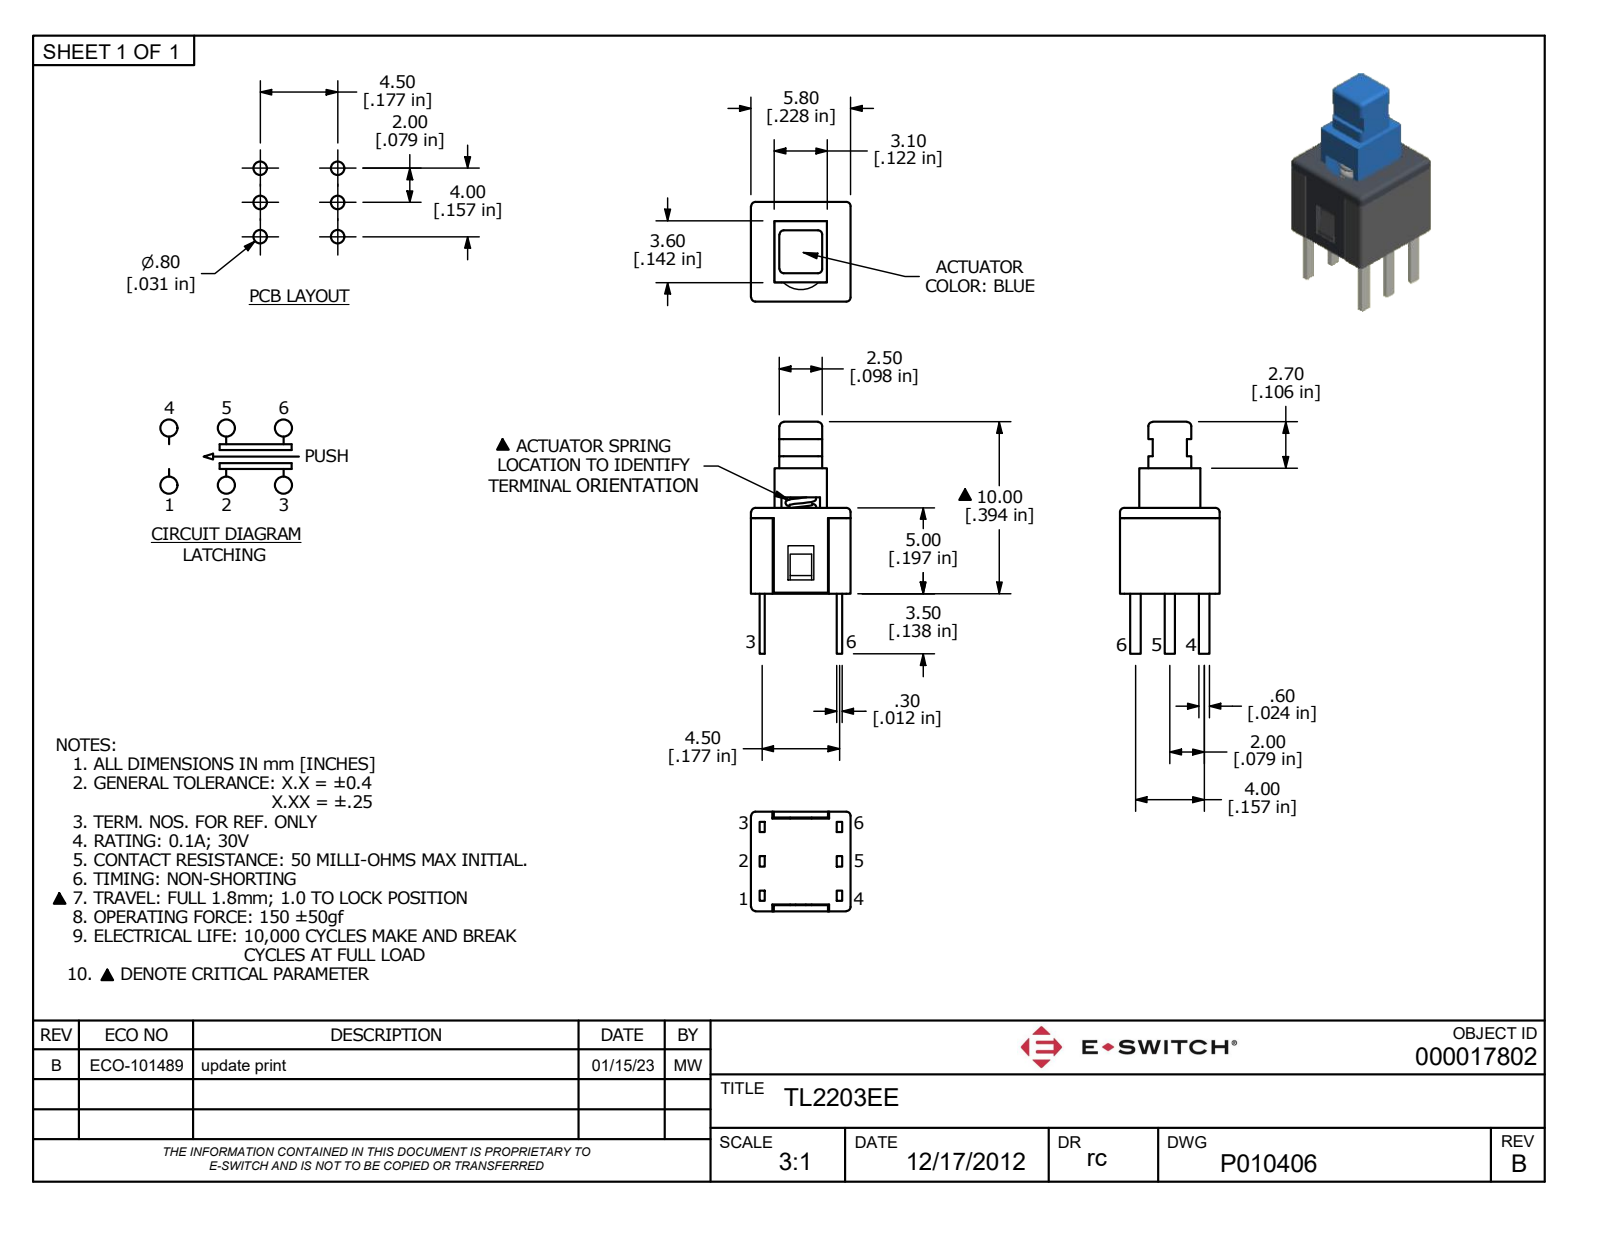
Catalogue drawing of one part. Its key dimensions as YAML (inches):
part_name: "P:\\\\E-Switch Secure\\\\3D_MODELS_STP_FORMAT\\\\TL2203xx.stp"
step_written_by: "ACIS (CONFIG_CONTROL_DESIGN)"
units: inches
bodies: {solids: 1, faces: 180, planar: 149, cylindrical: 22, other: 9}
overall_size: [0.531, 0.228, 0.228]
volume: 0.009
surface_area: 0.851
partial_cylinders:
  - {radius: 0.008, count: 8}
  - {radius: 0.01, count: 8}
  - {radius: 0.044, count: 1}
  - {radius: 0.057, count: 1}
face_to_face_distances: [0.024, 0.016, 0.228, 0.197, 0.041, 0.189, 0.187, 0.013, 0.054, 0.174]
